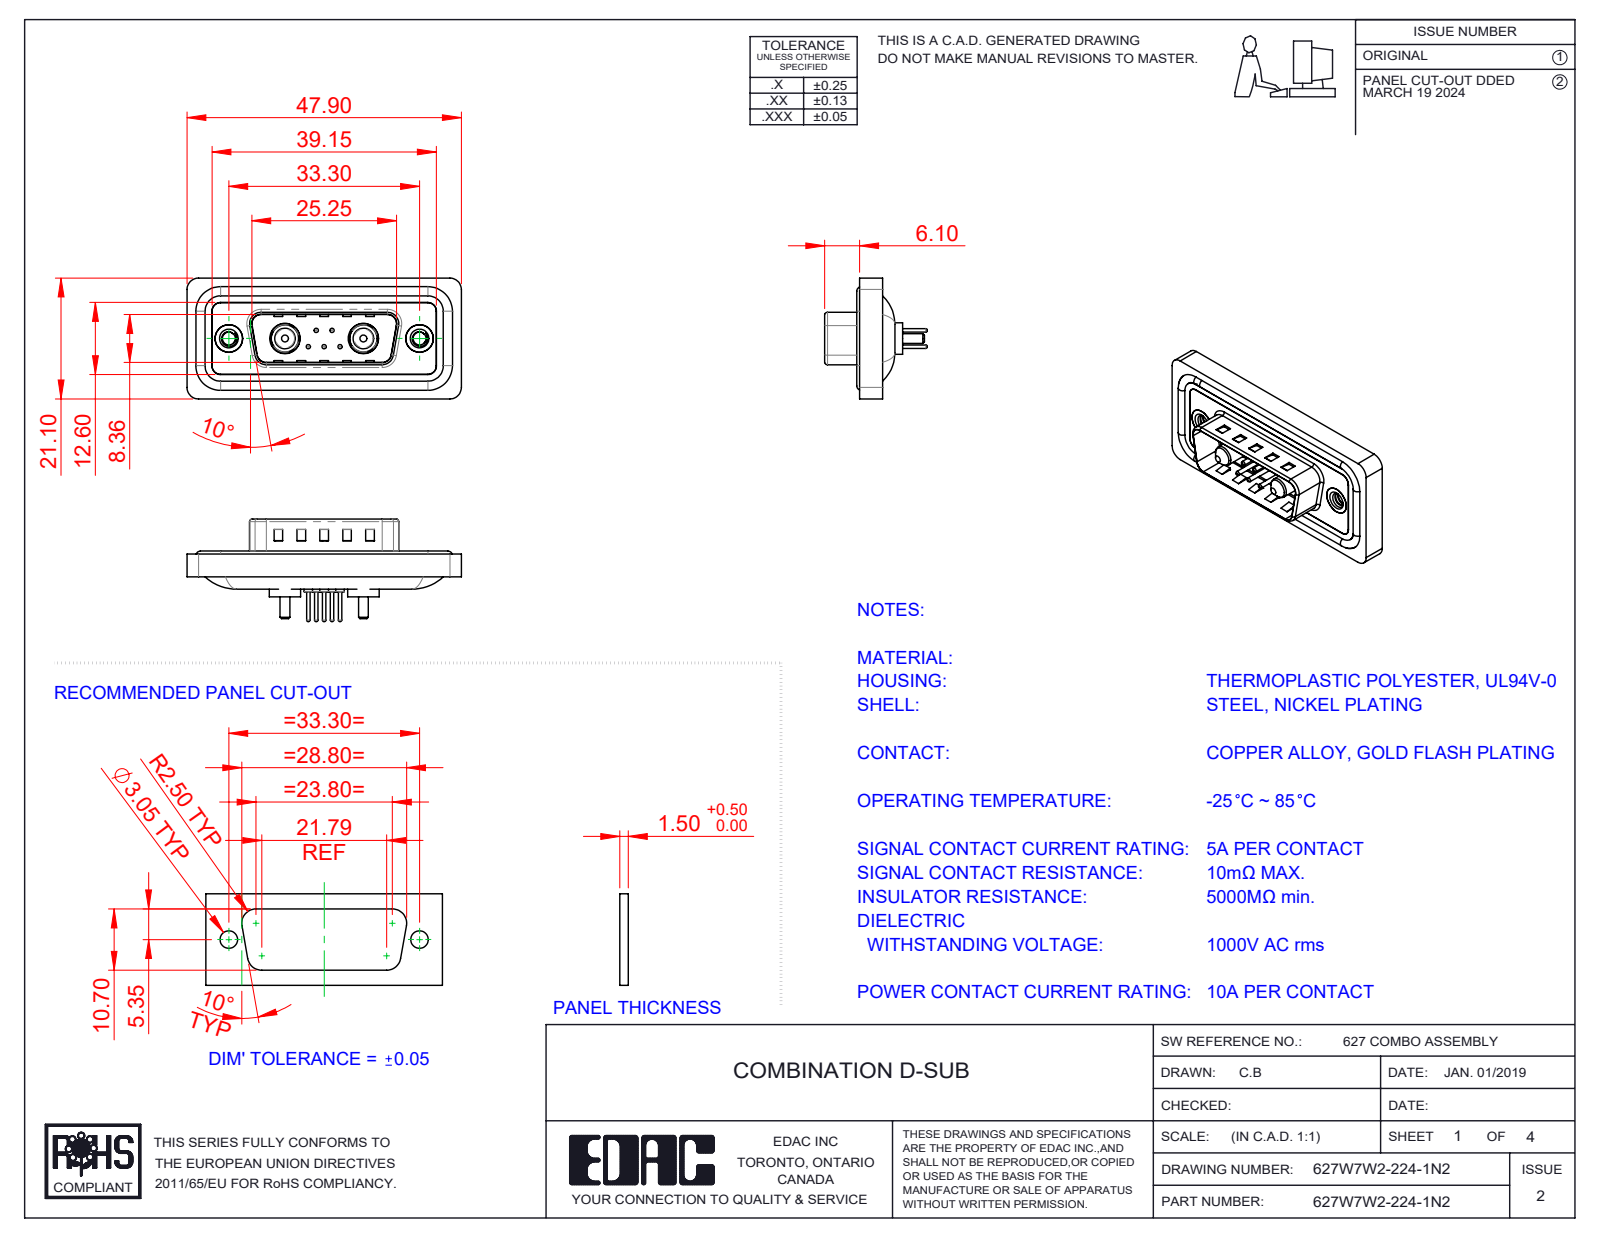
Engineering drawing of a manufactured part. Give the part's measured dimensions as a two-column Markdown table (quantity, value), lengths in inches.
| quantity | value |
| --- | --- |
| part name | 627Combo Waterproof Housing_15 Contacts; 627Combo Threaded Rivet_2; Power Pin_10A S; 627Combo Shell Rear_15 Contacts (+5 more) |
| STEP written by | SolidWorks 2023 (CONFIG_CONTROL_DESIGN) |
| units | inches |
| bodies | 16 solids, 710 faces (232 planar, 292 cylindrical, 186 other) |
| overall size | 1.886 × 0.831 × 0.705 |
| volume | 0.335 in³ |
| surface area | 13.59 in² |
| round holes (diameter × count) | 0.03 × 5, 0.063 × 5, 0.079 × 5, 0.089 × 2, 0.157 × 2, 0.189 × 2, 0.191 × 2, 0.197 × 2, 0.209 × 2 |
| round bosses / shafts (diameter × count) | 0.059 × 5, 0.024 × 5, 0.063 × 4, 0.217 × 2, 0.205 × 2, 0.193 × 2, 0.187 × 2, 0.148 × 2 |
| partial cylindrical surfaces (radius × count) | 0.059 × 26, 0.079 × 20, 0.02 × 8, 0.063 × 8, 0.01 × 4, 0.024 × 4, 0.026 × 4, 0.035 × 4 |
| main face-to-face distances | 0.016, 0.043, 0.059, 0.063, 0.02, 0.122, 0.114, 0.157, 0.032, 0.377 |
| hole center spacings | 0.124, 0.109, 0.386, 0.925, 0.17, 0.17, 0.198, 0.198 |
